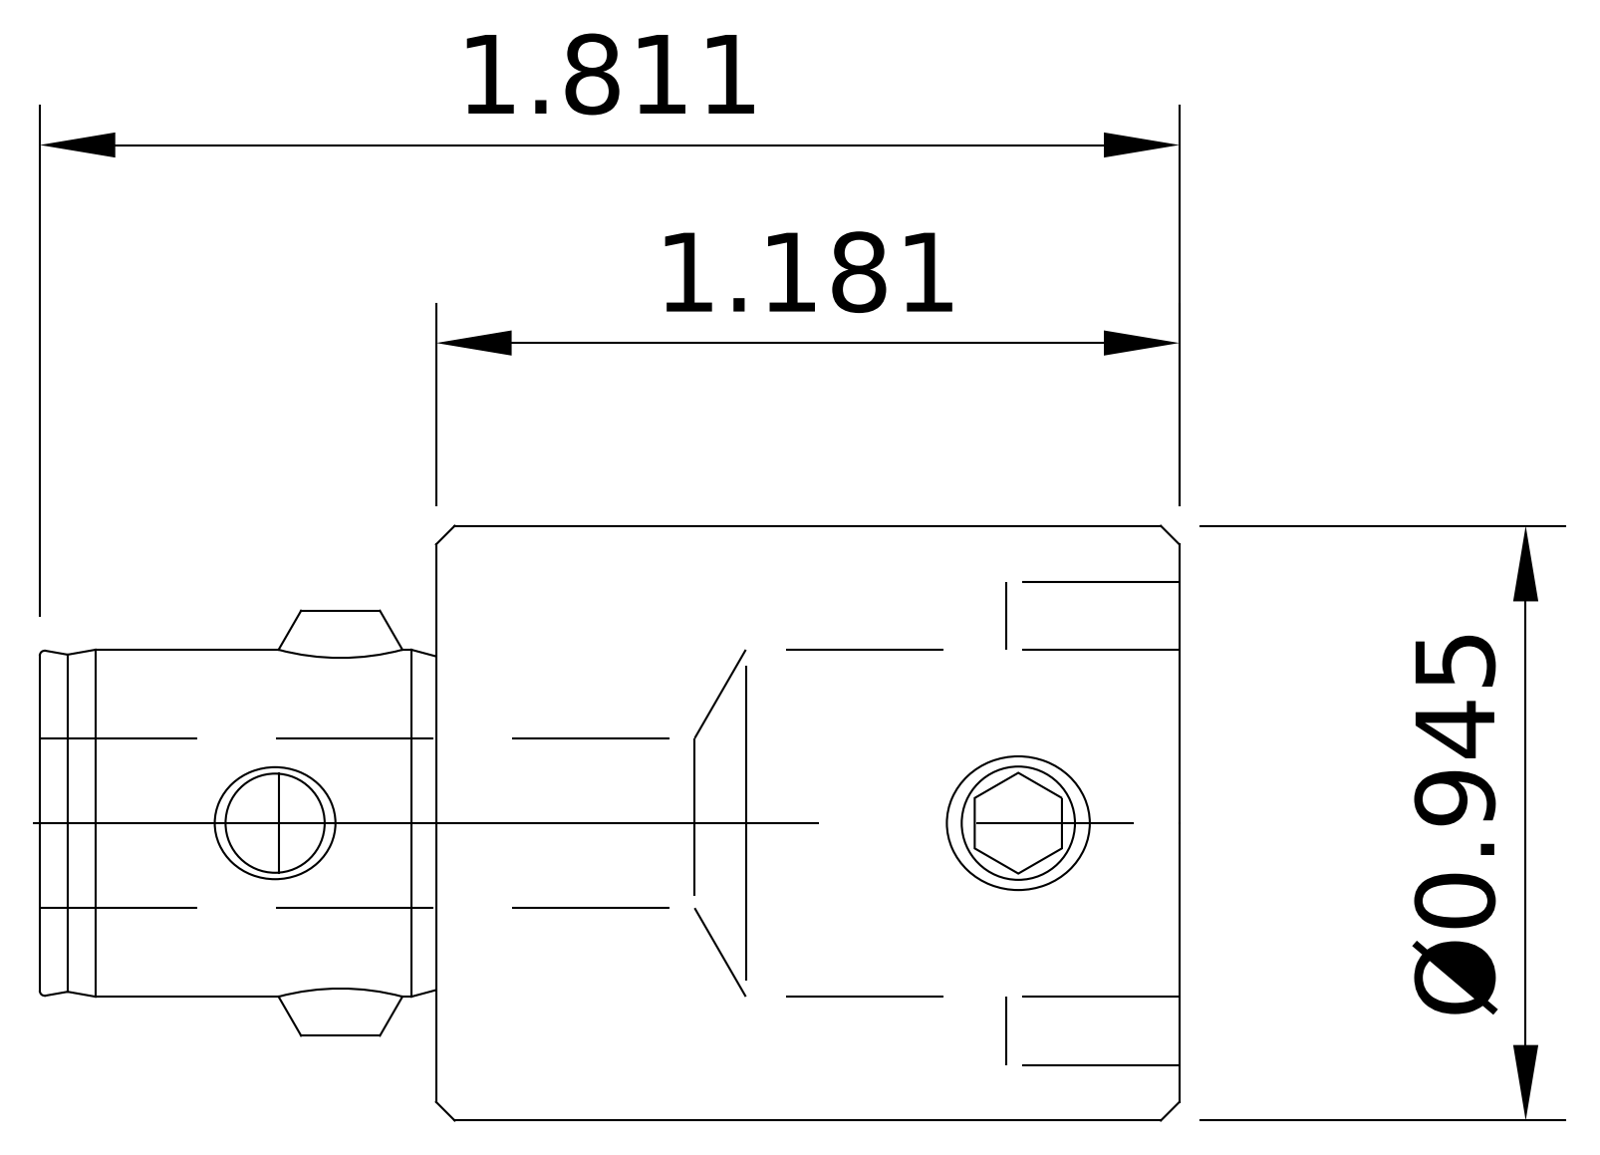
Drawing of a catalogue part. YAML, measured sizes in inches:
part_name: "10.691.50X_10.691.502; 11.331.220; 11.331.220_11.331.220; 10.690.43X_10.690.432 (+1 more)"
step_written_by: "SolidWorks 2015 (AUTOMOTIVE_DESIGN)"
units: inches
bodies: {solids: 4, faces: 122, planar: 35, cylindrical: 40, other: 47}
overall_size: [1.811, 0.945, 0.945]
volume: 0.731
surface_area: 8.914
round_holes:
  - {diameter: 0.138, count: 1}
  - {diameter: 0.157, count: 1}
  - {diameter: 0.165, count: 1}
  - {diameter: 0.197, count: 1}
  - {diameter: 0.205, count: 1}
  - {diameter: 0.276, count: 1}
  - {diameter: 0.551, count: 1}
  - {diameter: 0.571, count: 1}
round_bosses_or_shafts:
  - {diameter: 0.945, count: 1}
  - {diameter: 0.197, count: 1}
  - {diameter: 0.193, count: 1}
  - {diameter: 0.126, count: 1}
partial_cylinders:
  - {radius: 0.079, count: 2}
  - {radius: 0.276, count: 1}
face_to_face_distances: [1.181, 0.63, 1.811, 0.464, 1.539, 0.909, 0.272, 0.039, 0.128, 0.122]
hole_center_spacings: [1.169]
